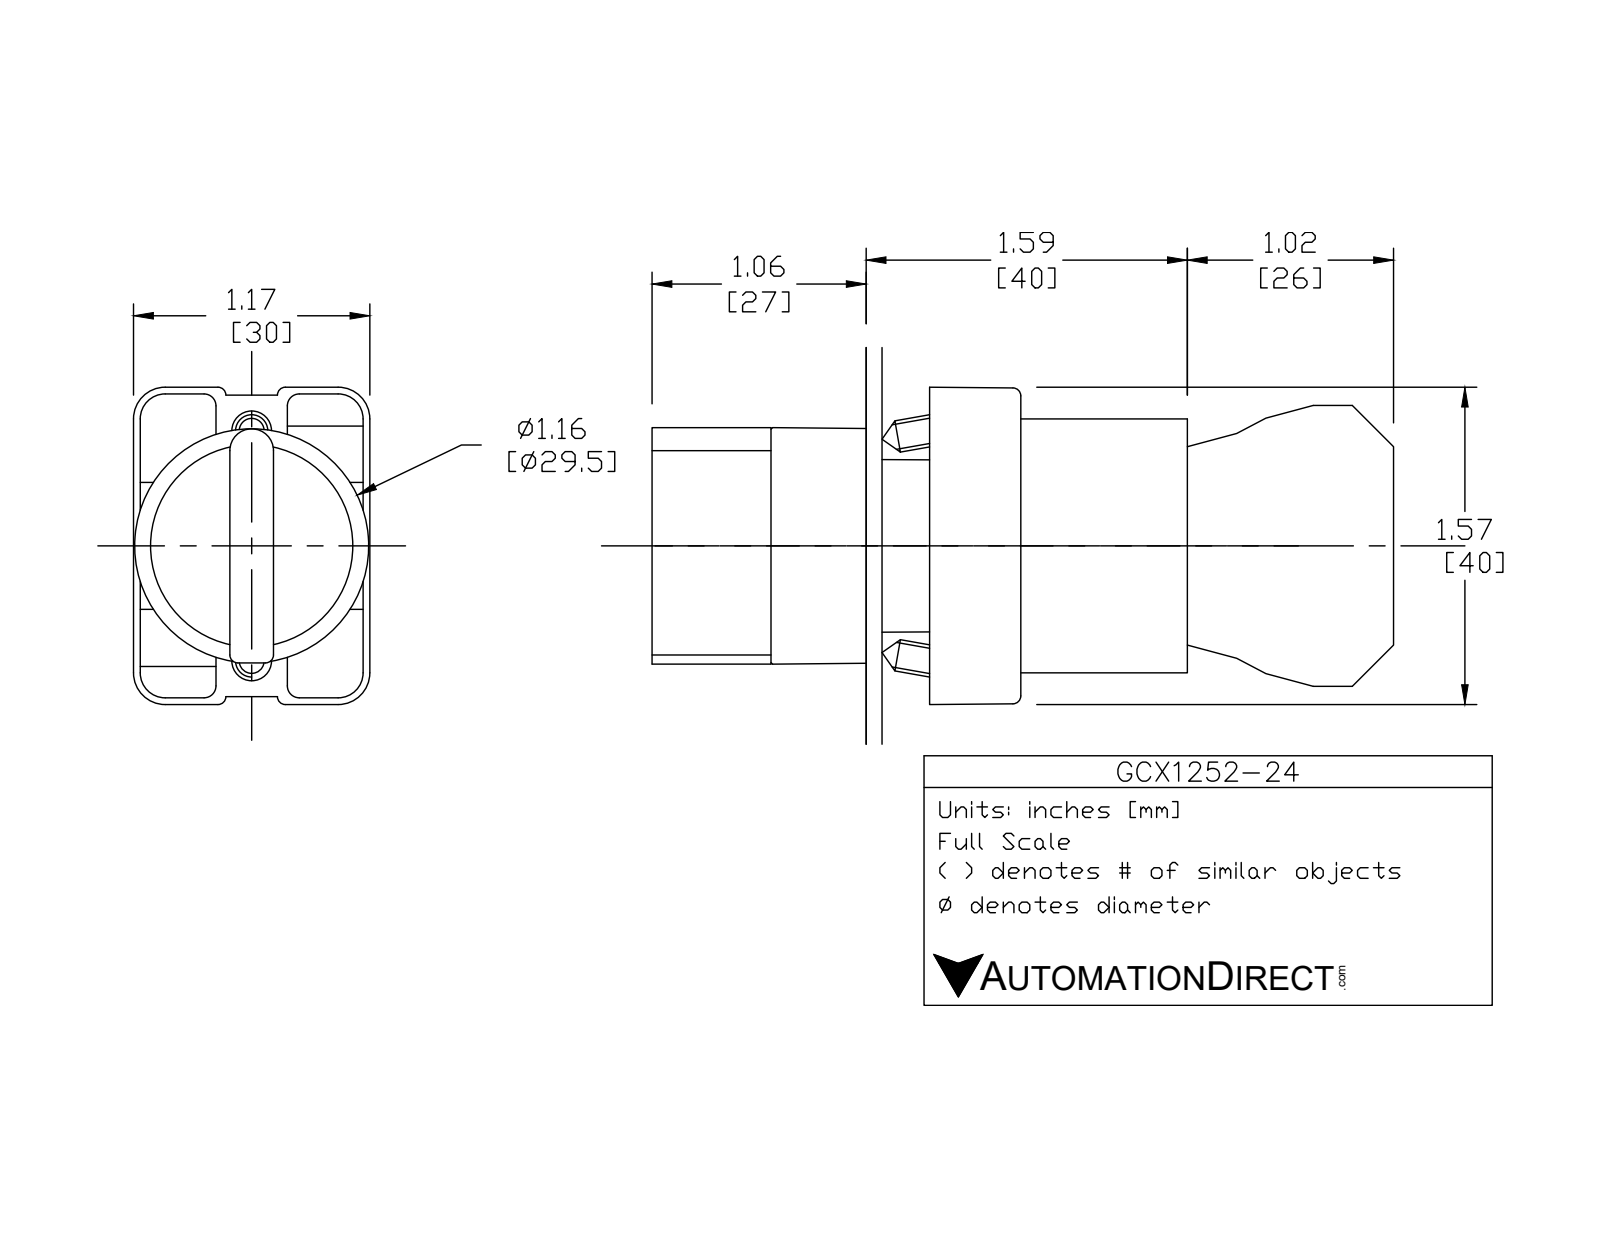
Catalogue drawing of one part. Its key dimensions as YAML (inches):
part_name: "ecx1029; ECX1050; GCX1252 OPERATOR; ecx1040 (+1 more)"
step_written_by: "SolidWorks 2016 (AUTOMOTIVE_DESIGN)"
units: inches
bodies: {solids: 8, faces: 445, planar: 263, cylindrical: 151, other: 31}
overall_size: [3.653, 1.581, 1.177]
volume: 2.799
surface_area: 39
round_holes:
  - {diameter: 0.079, count: 2}
  - {diameter: 0.124, count: 2}
  - {diameter: 0.13, count: 2}
  - {diameter: 0.087, count: 1}
  - {diameter: 0.197, count: 1}
  - {diameter: 0.469, count: 1}
  - {diameter: 0.878, count: 1}
  - {diameter: 0.888, count: 1}
  - {diameter: 1.024, count: 1}
round_bosses_or_shafts:
  - {diameter: 0.157, count: 4}
  - {diameter: 1.175, count: 1}
  - {diameter: 1.004, count: 1}
  - {diameter: 0.945, count: 1}
  - {diameter: 0.856, count: 1}
  - {diameter: 0.78, count: 1}
  - {diameter: 0.504, count: 1}
partial_cylinders:
  - {radius: 0.059, count: 24}
  - {radius: 0.041, count: 12}
  - {radius: 0.124, count: 12}
  - {radius: 0.157, count: 12}
  - {radius: 0.039, count: 9}
  - {radius: 0.128, count: 2}
  - {radius: 0.02, count: 1}
  - {radius: 0.063, count: 1}
face_to_face_distances: [0.827, 2.02, 1.193, 0.579, 1.244, 1.171, 0.472, 0.469, 0.031, 0.033]
hole_center_spacings: [0.236, 0.544, 0.472, 0.49]
